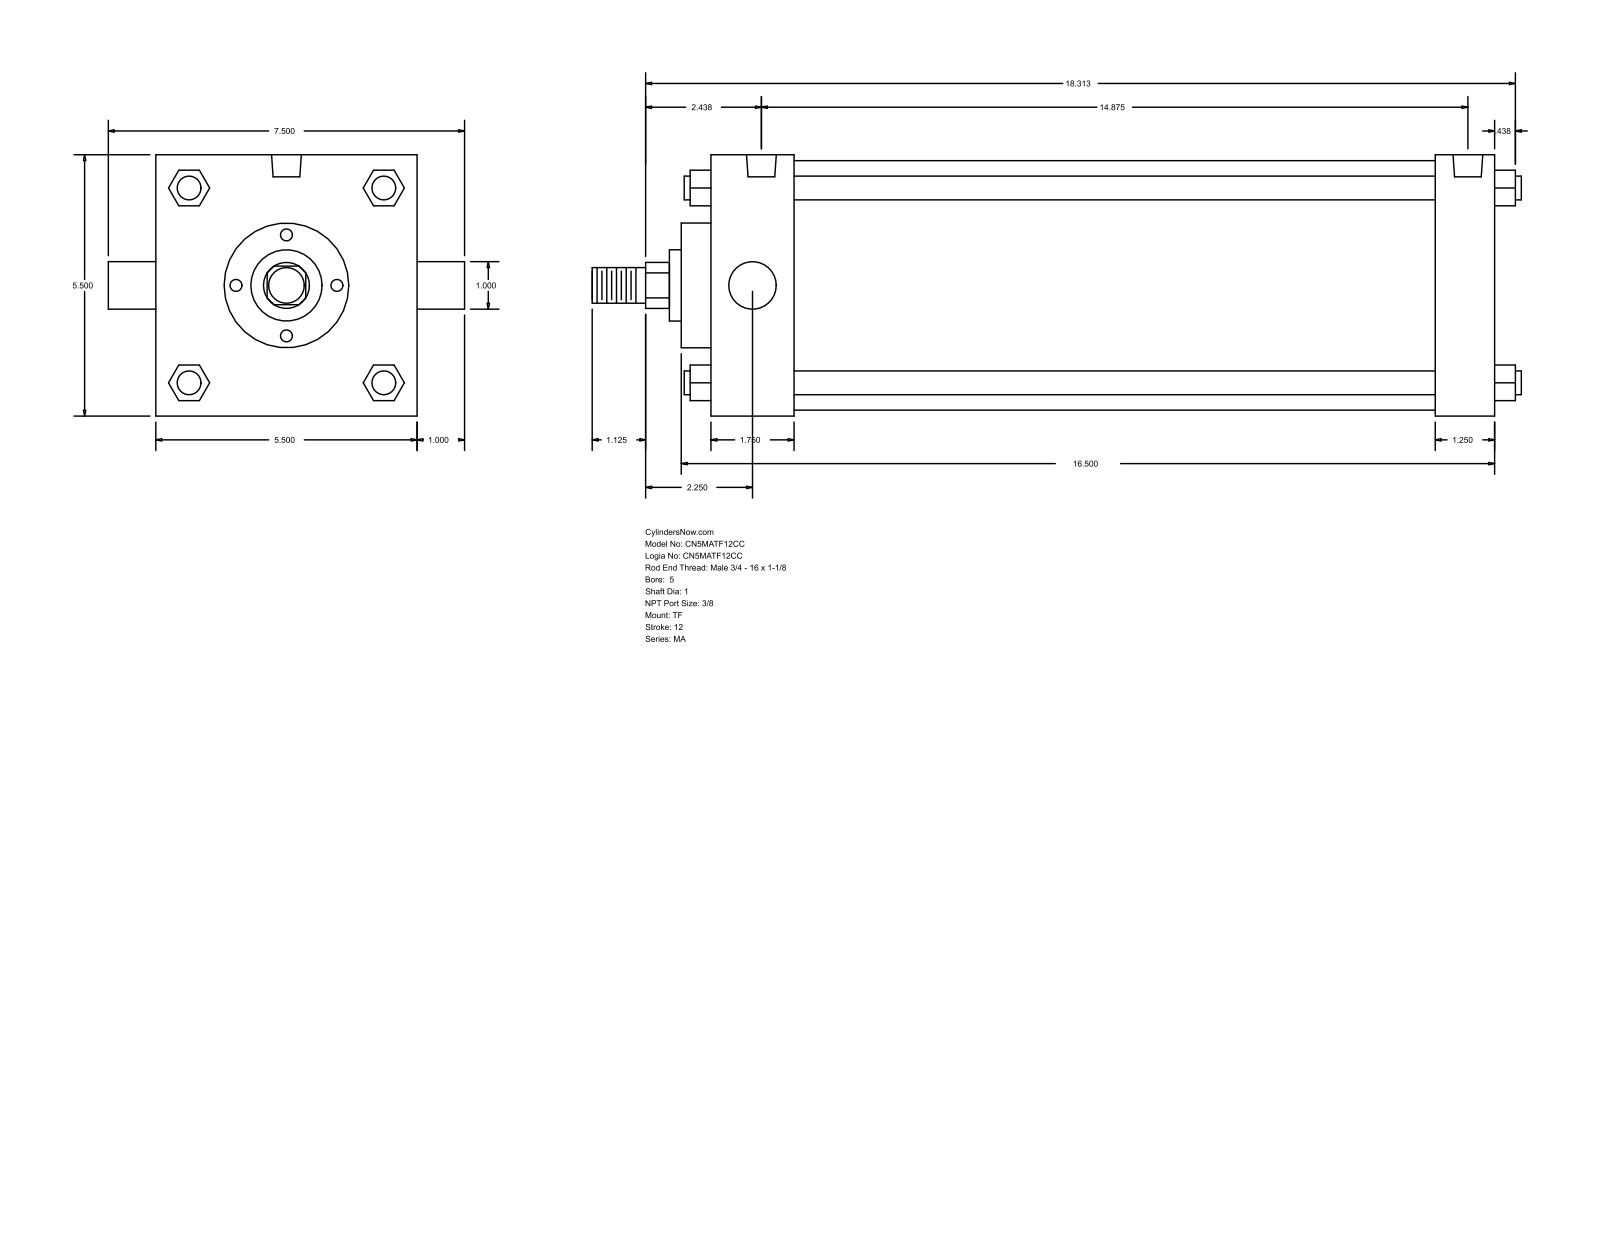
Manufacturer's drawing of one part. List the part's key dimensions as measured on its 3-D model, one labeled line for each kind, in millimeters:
Part name (STEP PRODUCT): MA_TF__0500_1
STEP written by: GSSL Pune (CONFIG_CONTROL_DESIGN)
Units: millimetres
Bodies: 0 solids, 122 faces (93 planar, 29 cylindrical, 0 other)
Overall size (bounding box): 496.89 × 190.5 × 139.7
Round holes (diameter × count): ⌀11.11 ×3, ⌀15.93 ×2
Round bosses / shafts (diameter × count): ⌀12.7 ×4, ⌀25.4 ×2, ⌀133.35 ×1, ⌀66.67 ×1, ⌀38.1 ×1, ⌀19.05 ×1
Partial cylindrical surfaces — rounded edges, fillets, slot ends (radius × count): R12.29 ×1
Main face-to-face distances: 139.7, 419.1, 387.35, 31.75, 44.46, 342.89, 374.64, 15.87, 60.33, 403.22
Hole centre spacings: 4.76, 373.07, 368.31, 377.83
